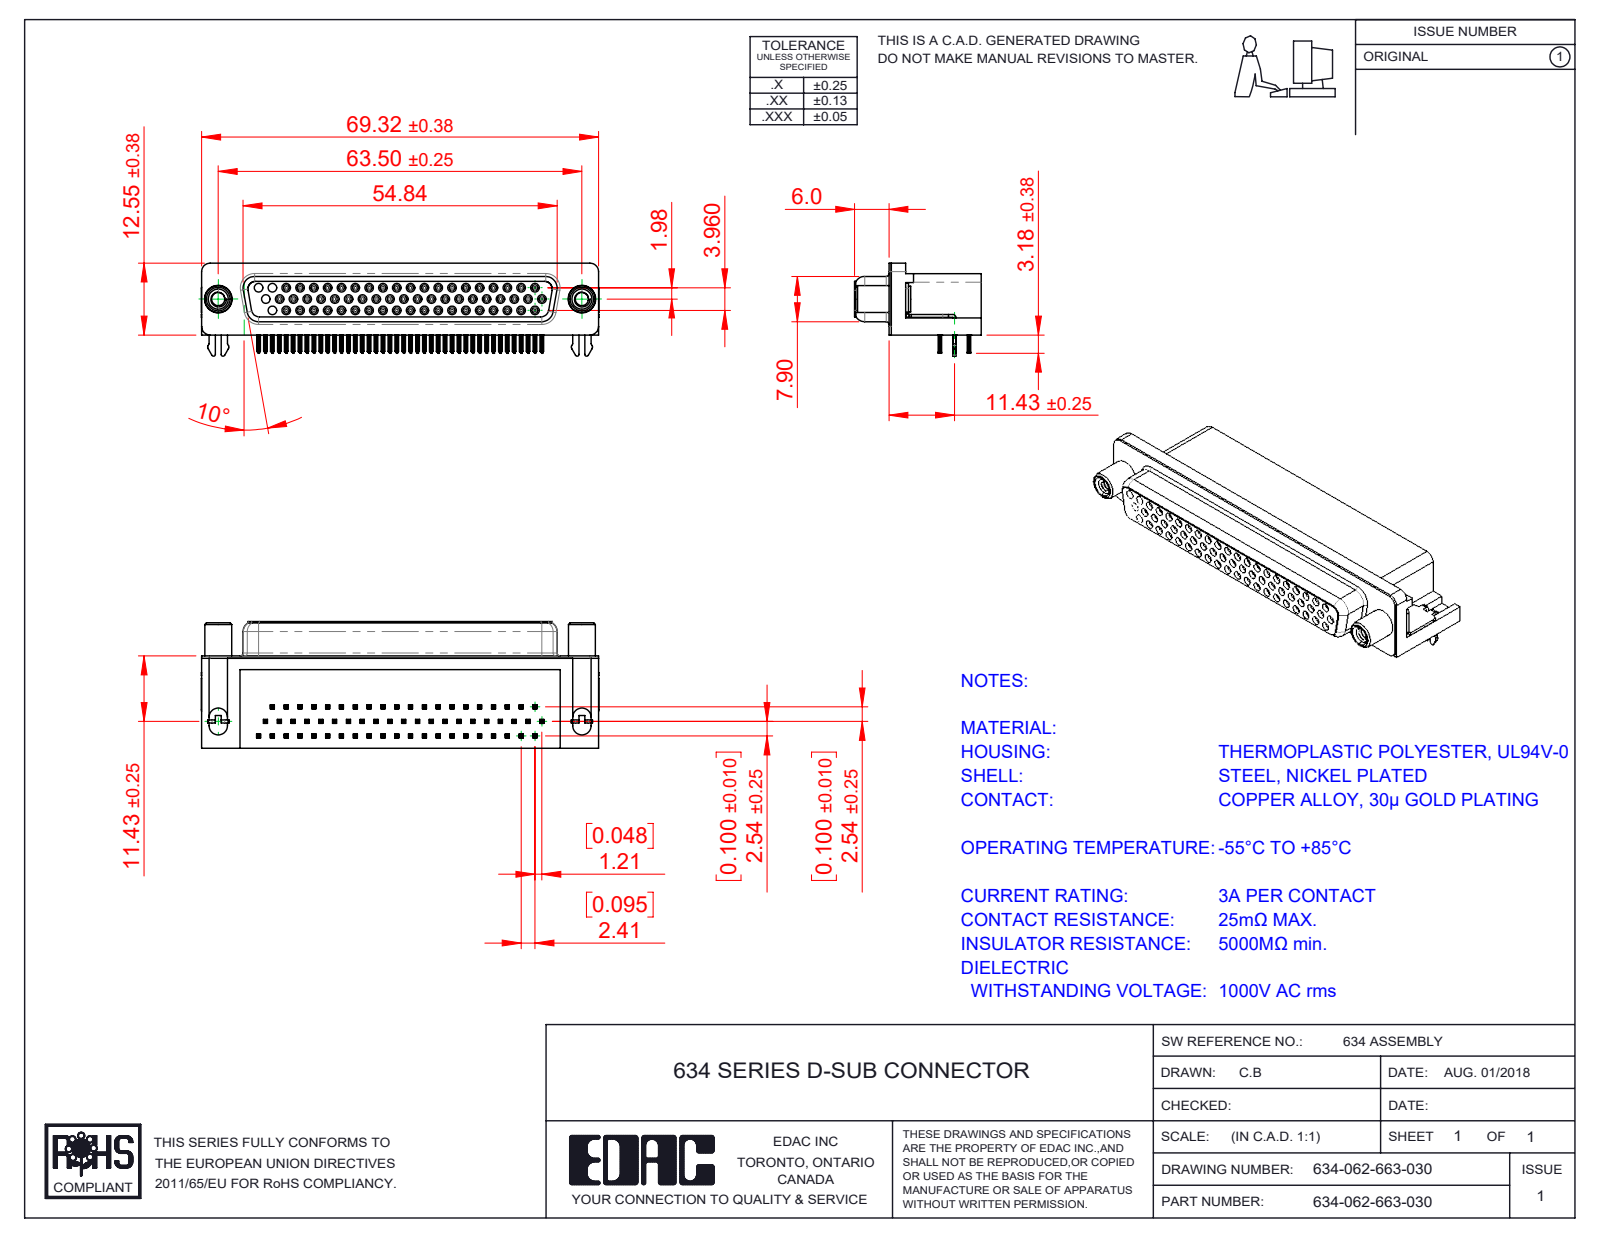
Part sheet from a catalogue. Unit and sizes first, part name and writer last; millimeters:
Units: millimetres
Overall size (bounding box): 69.4 × 22.1 × 16.25
Round holes (diameter × count): ⌀0.8 ×62, ⌀0.9 ×58, ⌀2.3 ×2, ⌀3.1 ×2, ⌀4 ×2, ⌀4.8 ×2, ⌀5 ×2
Round bosses / shafts (diameter × count): ⌀1.2 ×62, ⌀0.9 ×4, ⌀4.9 ×2, ⌀4.7 ×2, ⌀4.5 ×2, ⌀3.85 ×2
Partial cylindrical surfaces — rounded edges, fillets, slot ends (radius × count): R0.1 ×496, R0.15 ×248, R0.35 ×124, R0.34 ×62, R0.28 ×20, R1 ×19, R0.5 ×10, R1.35 ×8
Main face-to-face distances: 0.4, 10.35, 15.7, 1.98, 0.6, 7.05, 0.85, 6.65, 0.45, 9.03
Hole centre spacings: 4.82, 12.05, 4.64, 7.23, 8.25, 9.65, 16.89, 17.35
Volume: 13 033 mm³ · Surface area: 17 956 mm²
Bodies: 72 solids, 9131 faces (4115 planar, 2070 cylindrical, 2946 other)
Part name (STEP PRODUCT): 634 Shell_62 Socket; 634-062-663-030; Round Threaded Standoff; 2 Prong Board Lock (+4 more)
STEP written by: SolidWorks 2016 (CONFIG_CONTROL_DESIGN)
